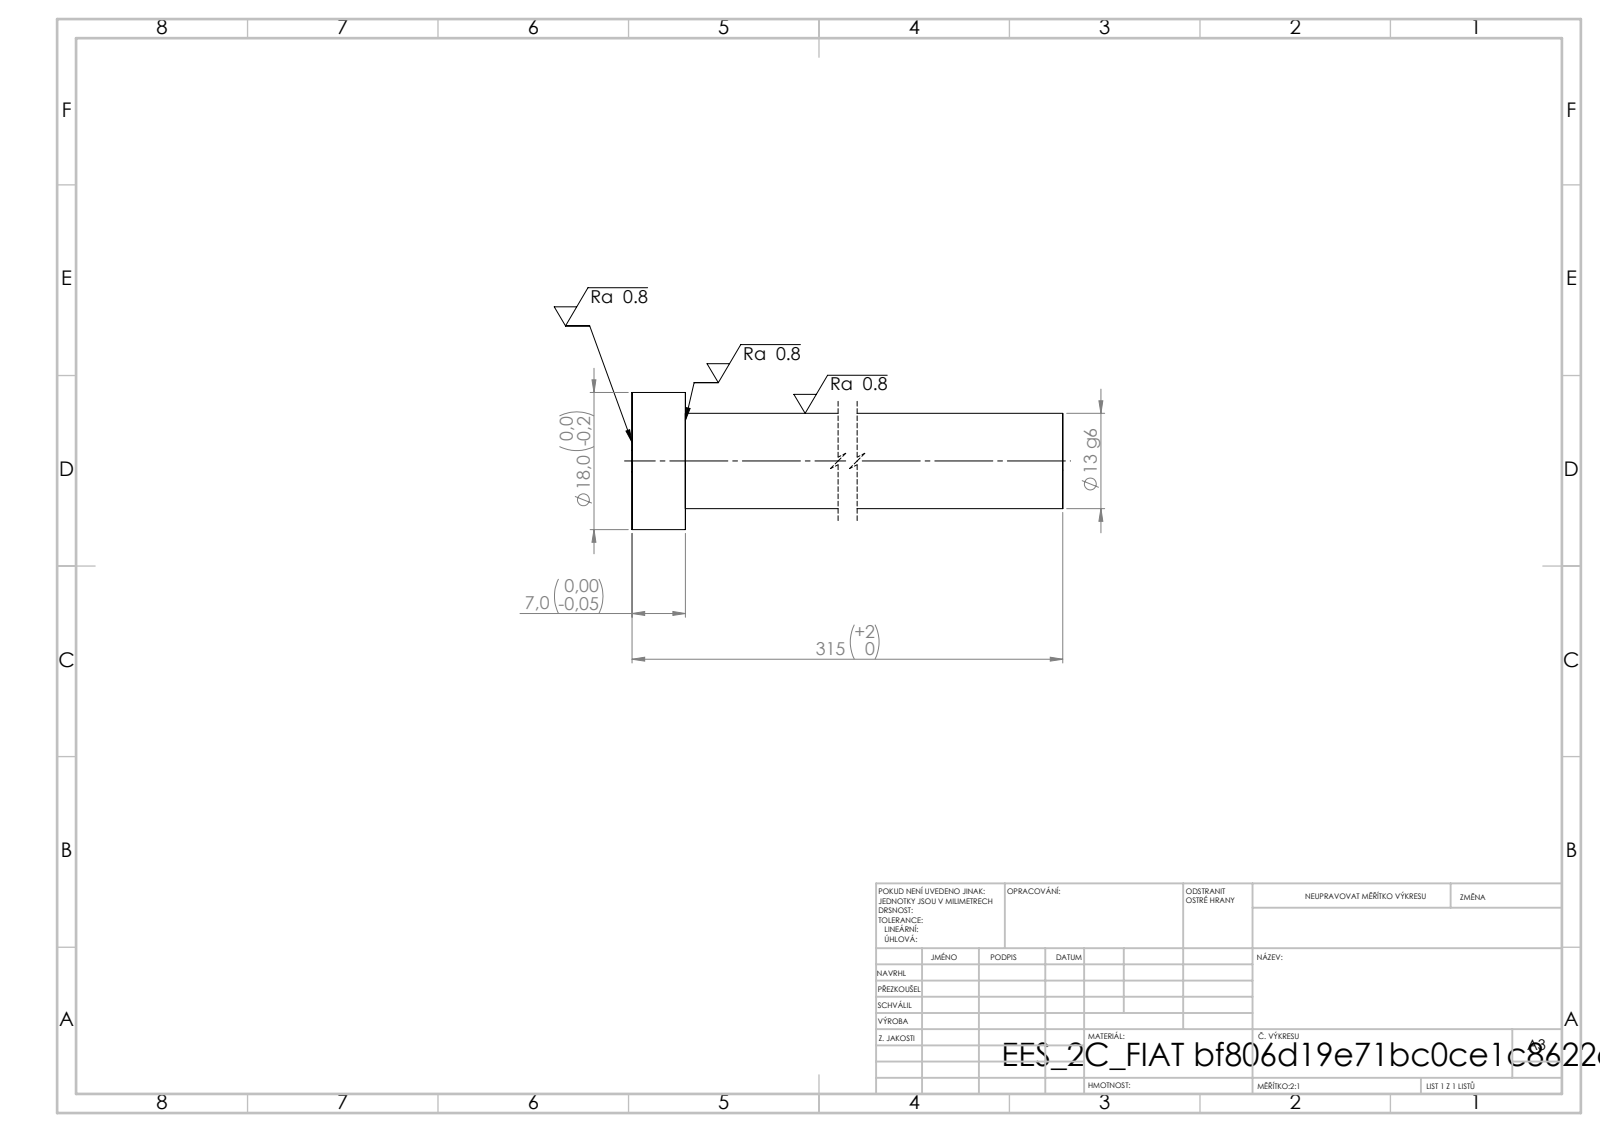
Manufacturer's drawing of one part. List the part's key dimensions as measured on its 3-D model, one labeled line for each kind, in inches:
STEP written by: SolidWorks 2019 (CONFIG_CONTROL_DESIGN)
Units: inches
Bodies: 1 solid, 7 faces (3 planar, 4 cylindrical, 0 other)
Overall size (bounding box): 12.402 × 0.709 × 0.709
Volume: 2.415 in³ · Surface area: 20.15 in²
Round bosses / shafts (diameter × count): ⌀0.709 ×1, ⌀0.492 ×1
Main face-to-face distances: 0.276, 12.402, 12.126
